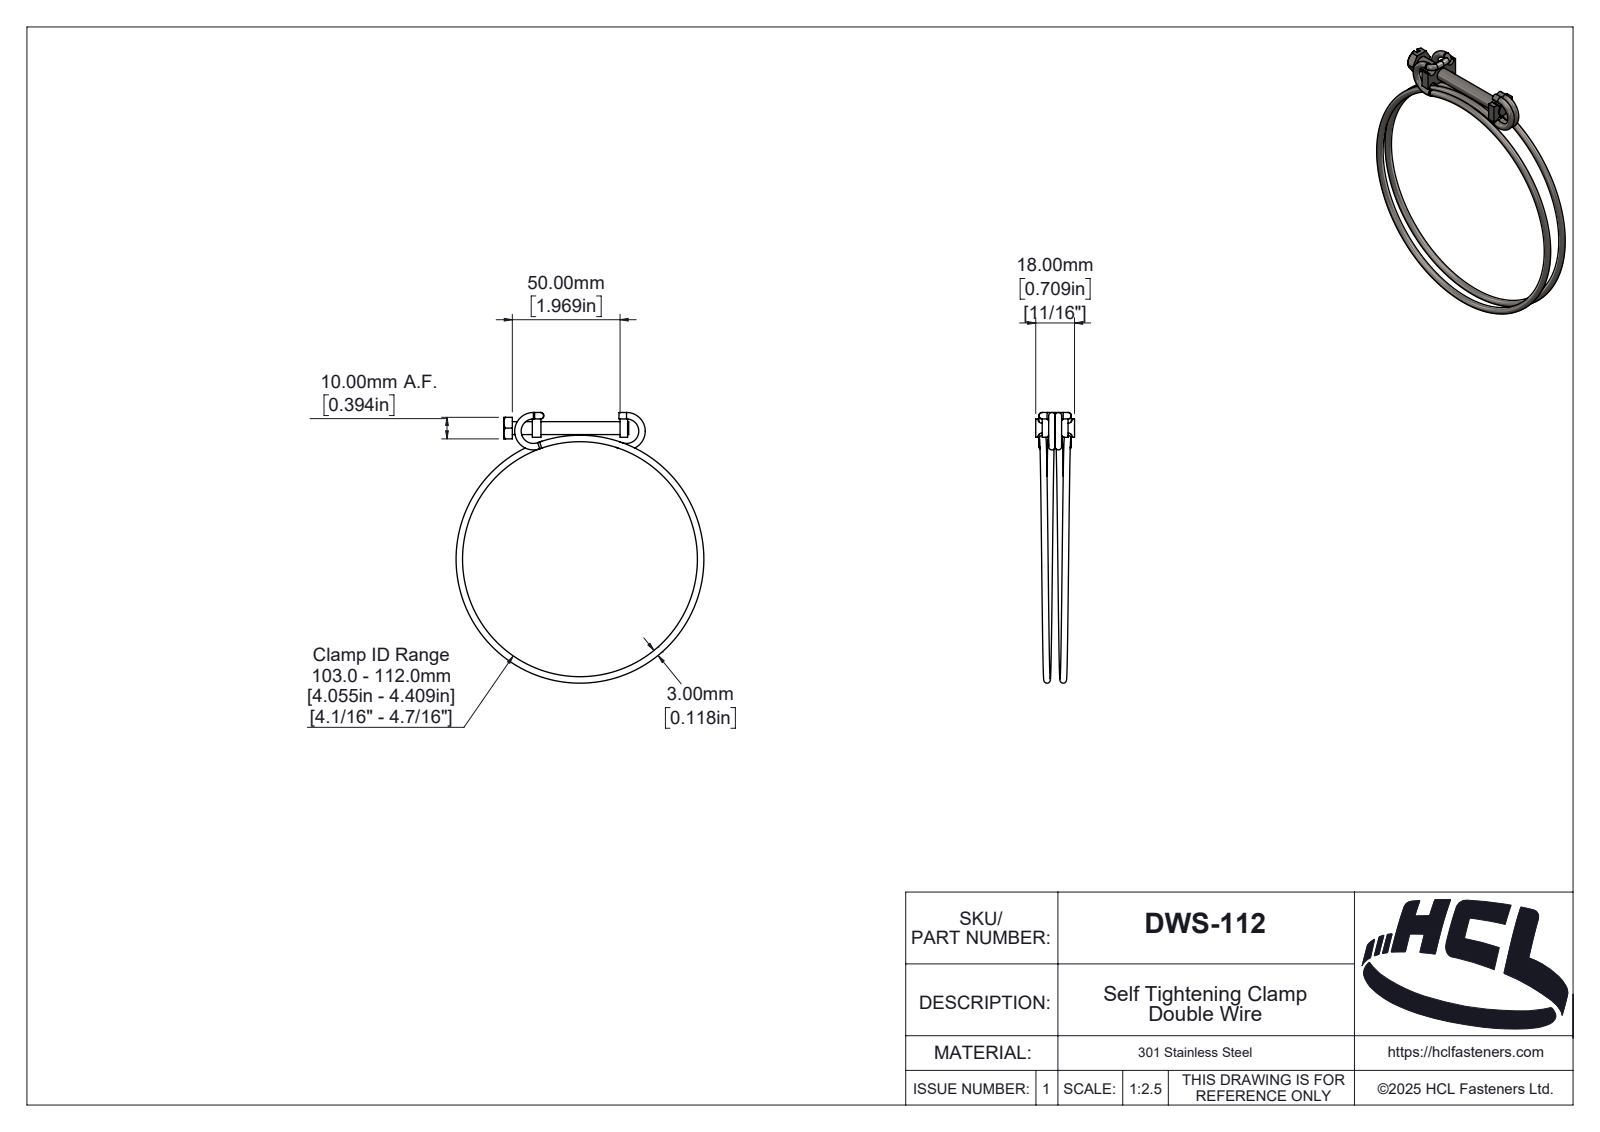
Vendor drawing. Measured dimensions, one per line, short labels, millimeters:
name: DWS-112
written by: SolidWorks 2025 (AUTOMOTIVE_DESIGN)
unit: mm
bodies: 6 solids, 213 faces (55 planar, 74 cylindrical, 84 other)
size: 125.55 × 115 × 18
volume: 8 838 mm³; area: 10 786 mm²
holes: 1× ⌀6
bosses: 4× ⌀3
rounds: 12× R0.2, 4× R1, 4× R2, 1× R0.4, 1× R0.51, 1× R0.53, 1× R0.64, 1× R0.91
face distances: 4, 13.28, 10, 40.72, 3, 54, 40.22, 53.5, 1, 36.72
